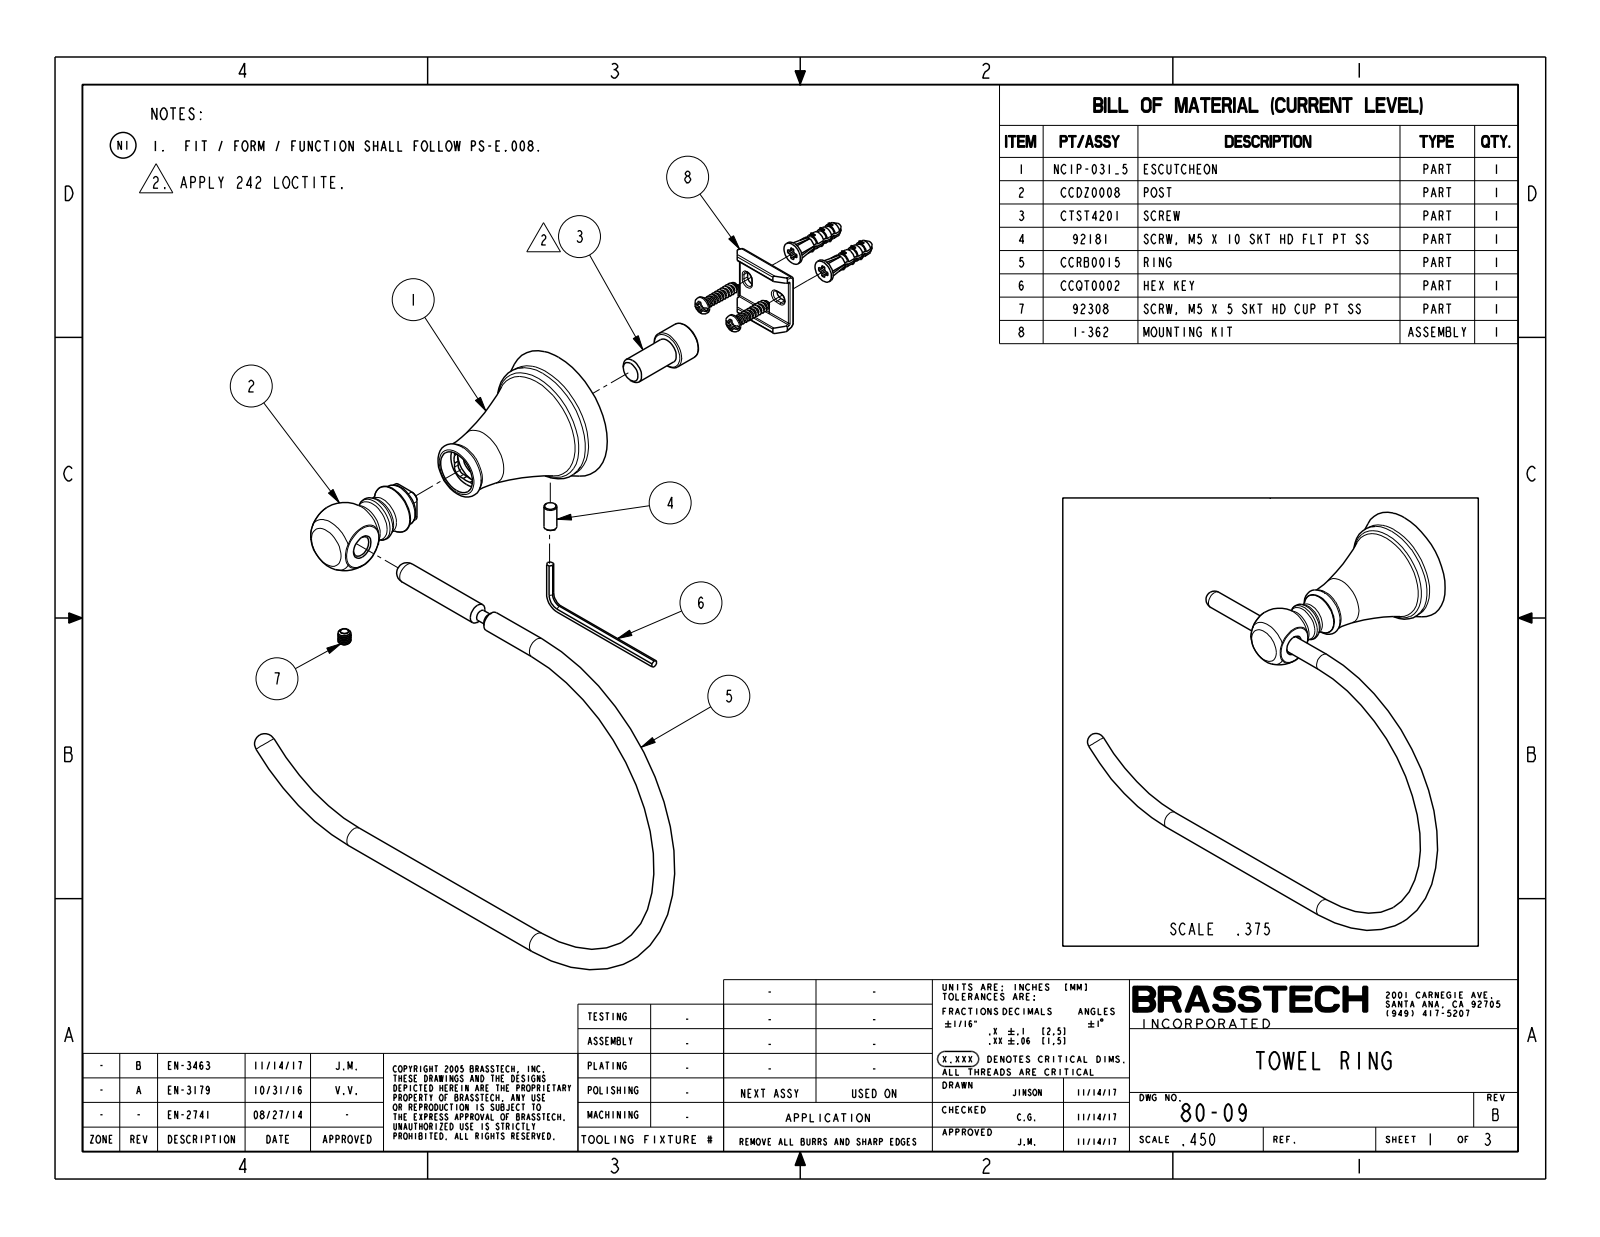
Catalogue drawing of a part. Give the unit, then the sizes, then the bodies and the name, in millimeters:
Units: millimetres
Overall size (bounding box): 226.8 × 170.7 × 94.5
Round holes (diameter × count): ⌀4.2 ×2, ⌀6 ×2, ⌀5.4 ×1, ⌀8.3 ×1, ⌀8.6 ×1, ⌀10 ×1, ⌀10.6 ×1, ⌀17 ×1, ⌀17.4 ×1, ⌀24 ×1, ⌀42.7 ×1, ⌀49 ×1
Round bosses / shafts (diameter × count): ⌀8 ×2, ⌀5 ×2, ⌀14.9 ×1, ⌀4.5 ×1
Partial cylindrical surfaces — rounded edges, fillets, slot ends (radius × count): R0.5 ×22, R3 ×8, R2 ×6, R2.3 ×4, R6.9 ×1
Main face-to-face distances: 2.5, 17.8, 15.3, 2.3, 15.5, 13.5, 2, 42.4, 31.4, 29.1
Hole centre spacings: 78
Volume: 56 400 mm³ · Surface area: 33 190 mm²
Bodies: 7 solids, 302 faces (92 planar, 94 cylindrical, 116 other)
Part name (STEP PRODUCT): NCIP-031_5; CCDZ0008; CTST4201; CCKT0030 (+4 more)
STEP written by: PRO/ENGINEER BY PARAMETRIC TECHNOLOGY CORPORATION, 2013150 (CONFIG_CONTROL_DESIGN)
